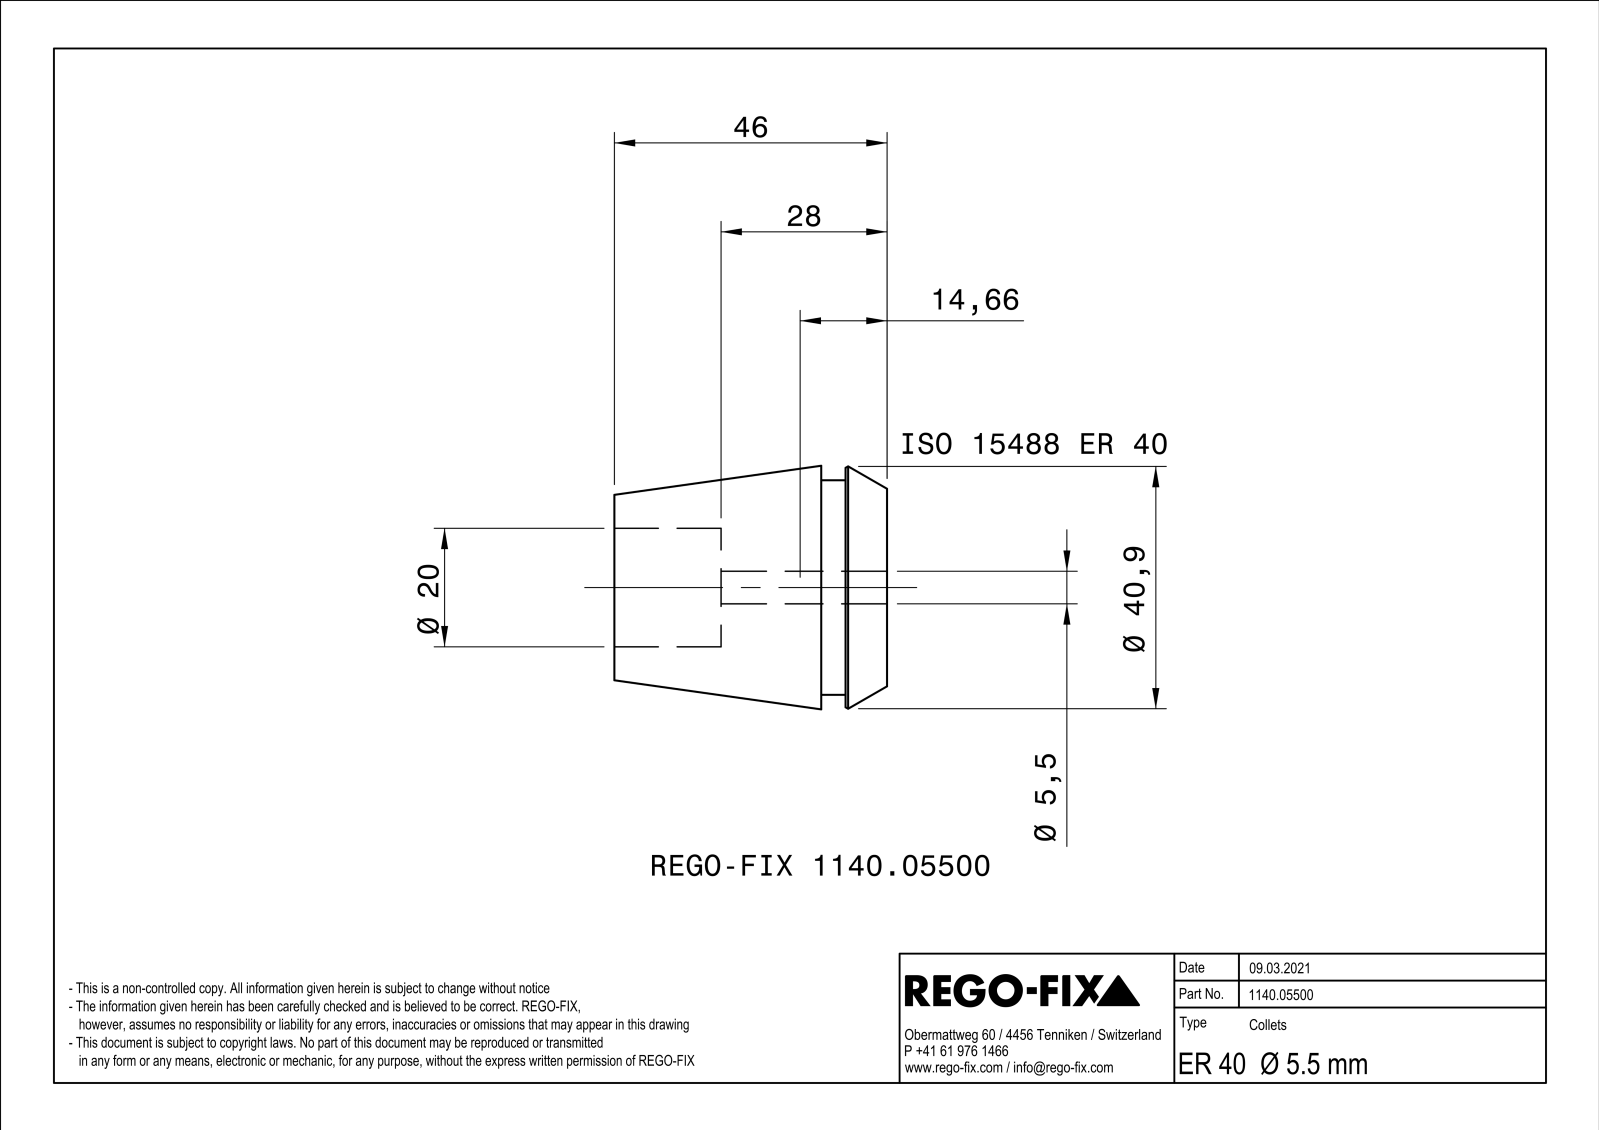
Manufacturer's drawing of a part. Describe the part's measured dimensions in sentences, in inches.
The part is named "NOCUT". Its 3-D file was written by "SIEMENS PLM Software Solid Edge ST10 (AUTOMOTIVE_DESIGN)". It is 1 solid with 272 faces: 104 planar, 48 cylindrical and 120 other. Overall it measures 1.811 by 1.618 by 1.618 inches. Its volume is 2.216 cubic inches and its surface area 33.35 square inches. Round holes: 1 of diameter 0.787. Round bosses or shafts: 1 of diameter 1.425. Partial cylindrical surfaces (rounded edges, fillets, slot ends): 8 of radius 1.772, 1 of radius 0.108. The main face-to-face distances are 0.031, 0.032, 0.031, 1.811, 0.437, 1.374, 0.276, 0.161, 1.535, 1.102.
